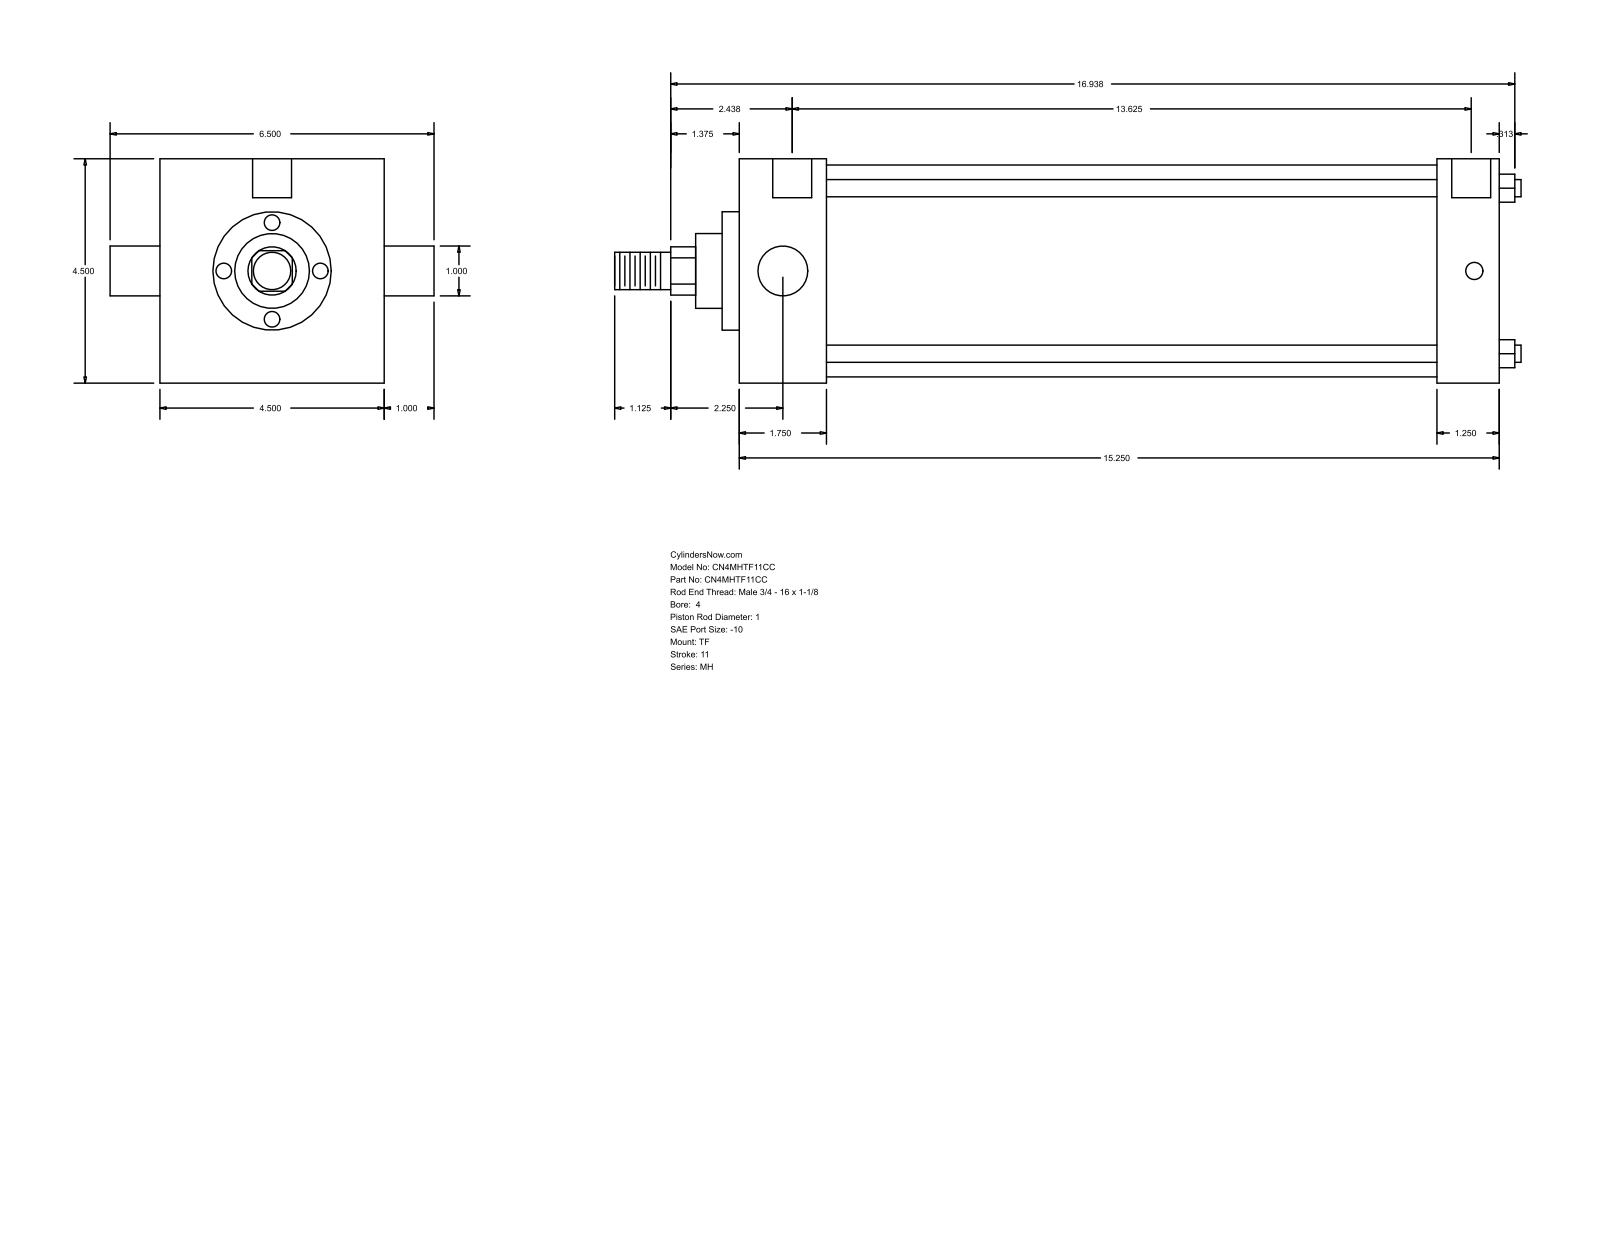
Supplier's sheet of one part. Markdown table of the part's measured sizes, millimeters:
| quantity | value |
| --- | --- |
| part name | MH_TF__0400_1 |
| STEP written by | GSSL Pune (CONFIG_CONTROL_DESIGN) |
| units | millimeters |
| bodies | 0 solids, 86 faces (61 planar, 25 cylindrical, 0 other) |
| overall size | 461.96 × 165.1 × 114.3 |
| round holes (diameter × count) | 8.73 × 3, 19.84 × 2 |
| round bosses / shafts (diameter × count) | 8.76 × 4, 25.4 × 2, 107.95 × 1, 60.33 × 1, 38.1 × 1, 19.05 × 1 |
| partial cylindrical surfaces (radius × count) | 12.29 × 1 |
| main face-to-face distances | 114.3, 387.35, 44.46, 342.89, 355.6, 311.14, 31.75, 8.73, 53.19, 364.33 |
| hole center spacings | 1.58, 347.66, 346.08, 349.24 |
